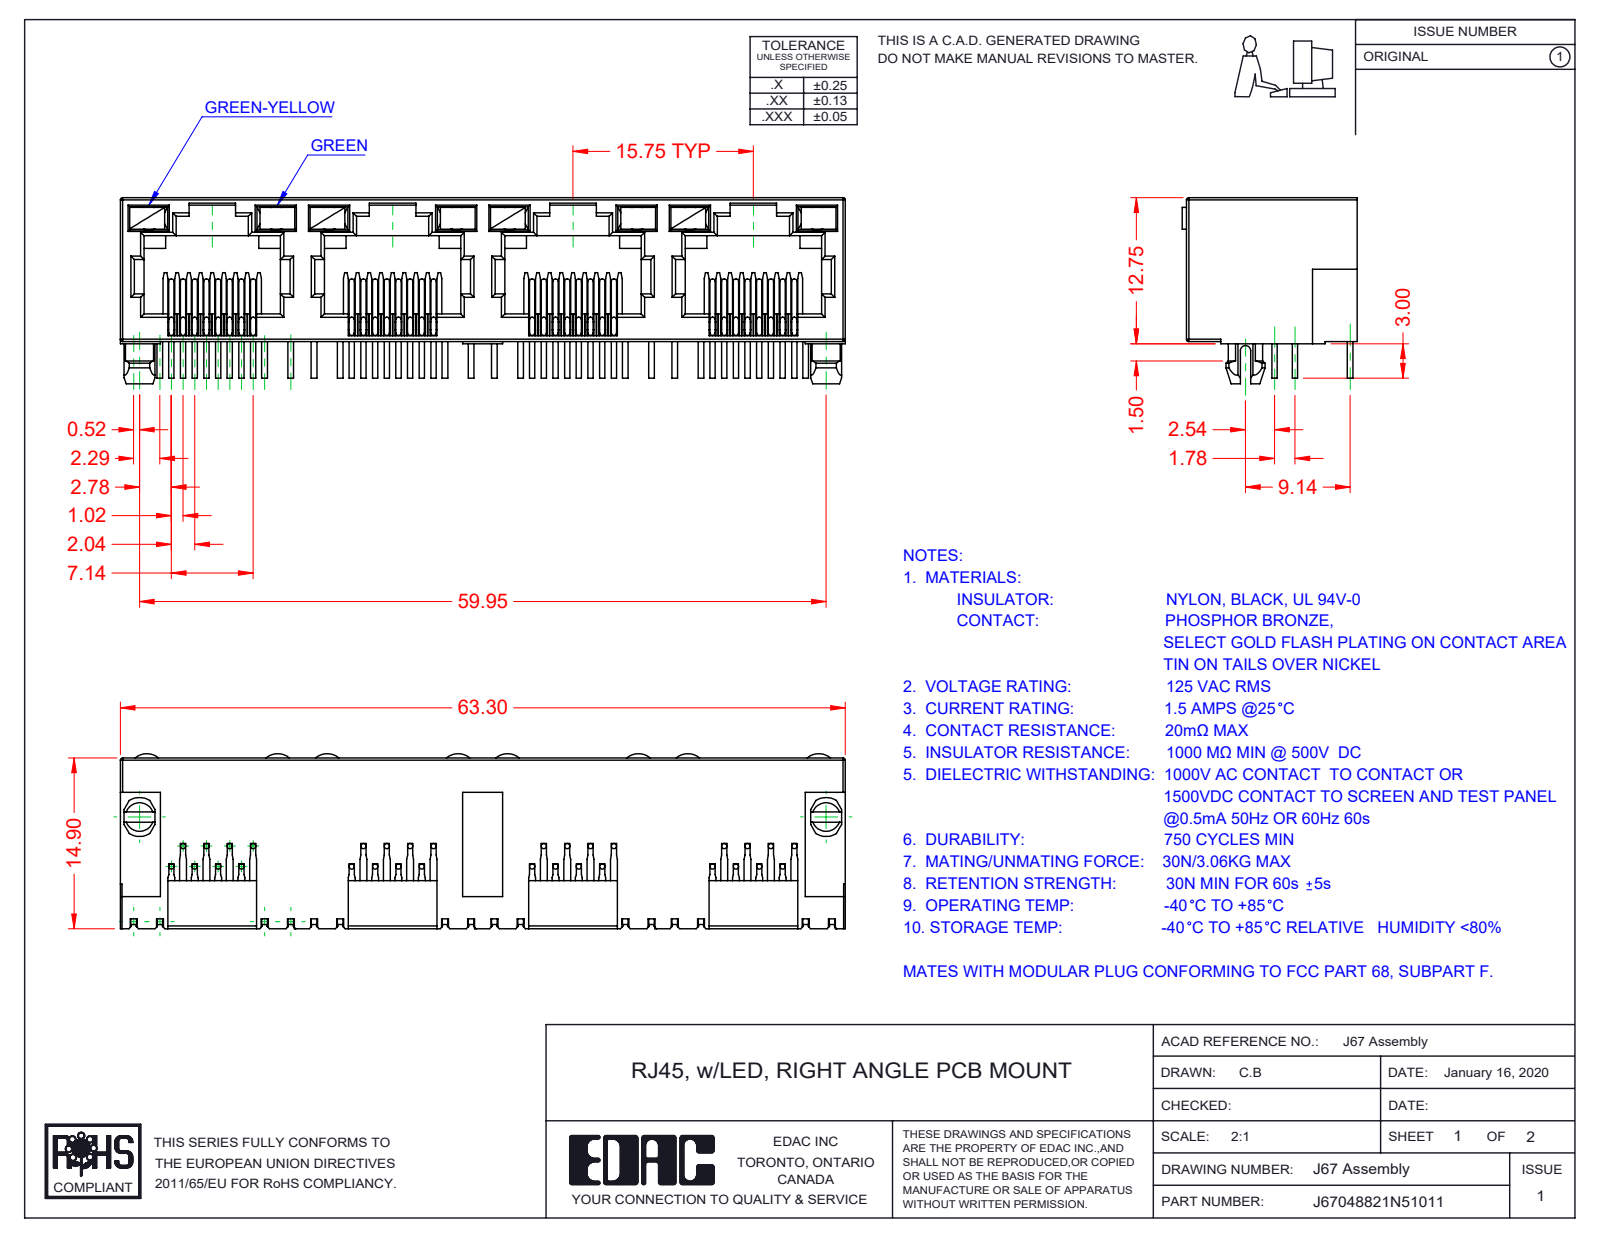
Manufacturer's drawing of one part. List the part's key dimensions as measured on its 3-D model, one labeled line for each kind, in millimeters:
Part name (STEP PRODUCT): J67048822N53011; 67 Insulator; 67 Contacts; 67 LED LH_5-Green-Yellow (+1 more)
STEP written by: SolidWorks 2016 (CONFIG_CONTROL_DESIGN)
Units: millimetres
Bodies: 41 solids, 2473 faces (1781 planar, 484 cylindrical, 208 other)
Overall size (bounding box): 63.3 × 16.25 × 15.28
Volume: 5 159 mm³ · Surface area: 11 573 mm²
Round bosses / shafts (diameter × count): ⌀0.46 ×96
Partial cylindrical surfaces — rounded edges, fillets, slot ends (radius × count): R0.2 ×66, R0.3 ×29, R0.45 ×9, R1.55 ×8, R1.5 ×2, R1.7 ×2, R0.35 ×1, R1 ×1
Main face-to-face distances: 0.5, 12.55, 1.89, 0.89, 10, 15.75, 1, 1.39, 11, 11.89
